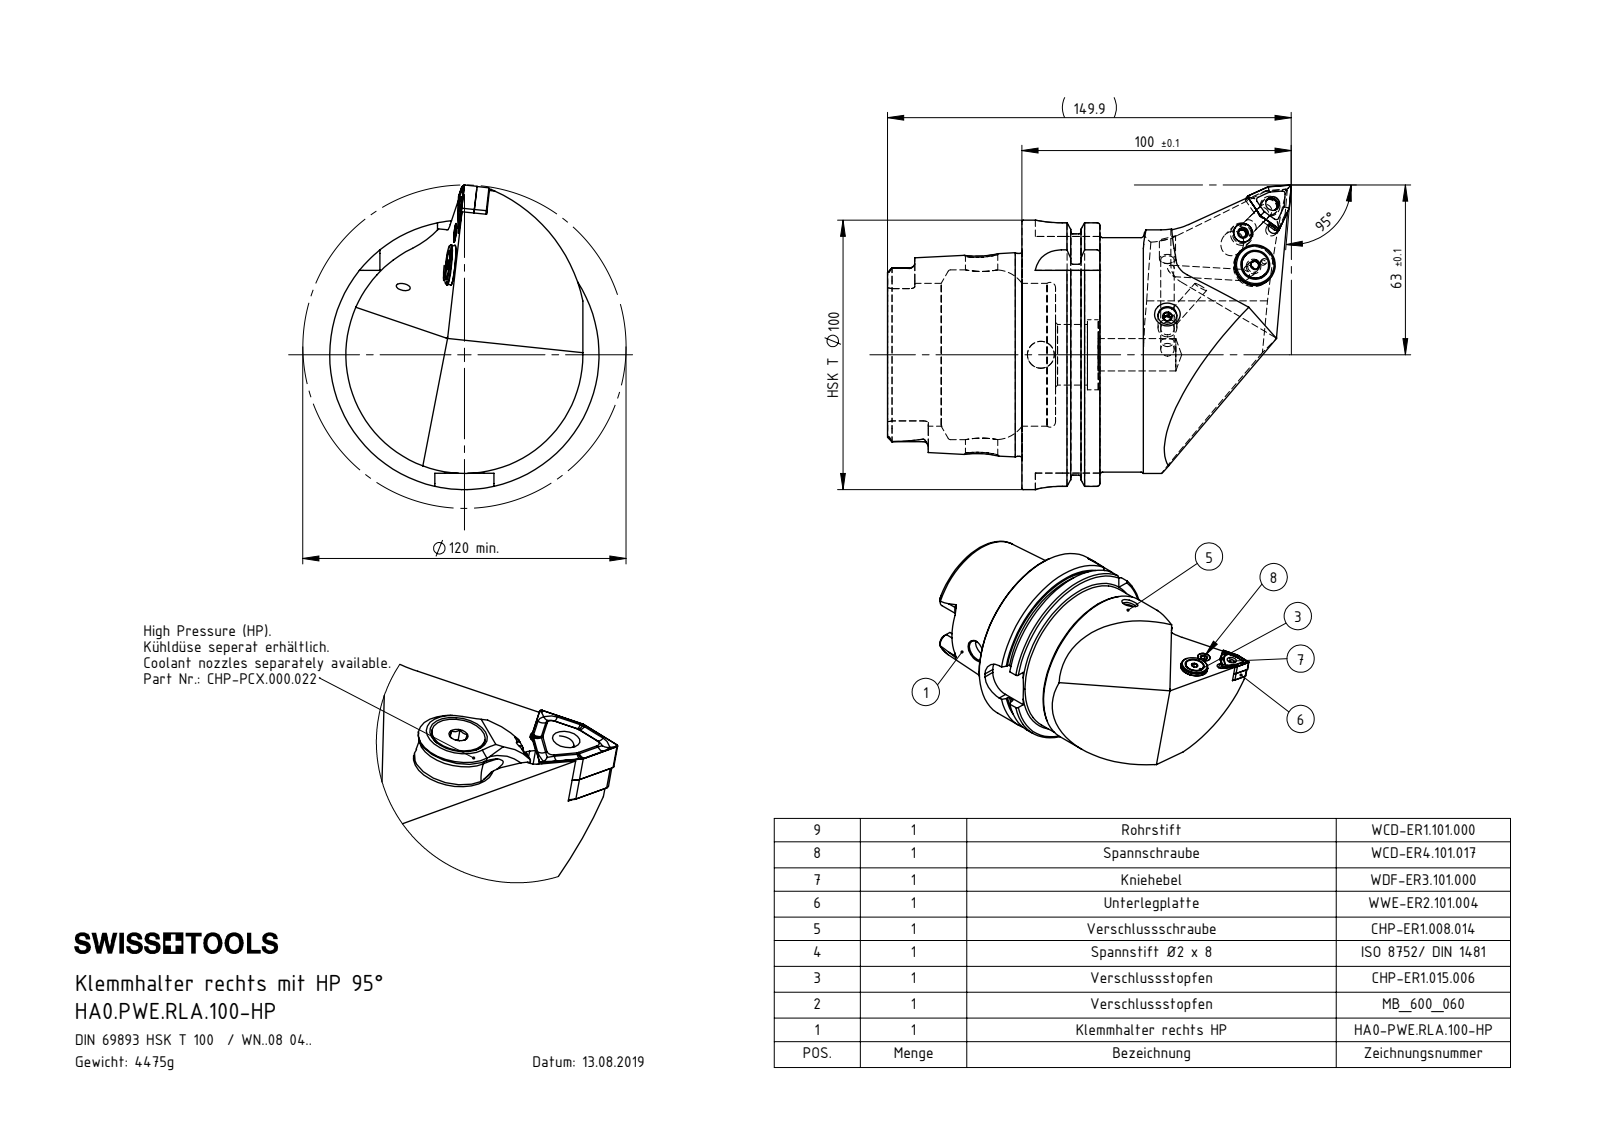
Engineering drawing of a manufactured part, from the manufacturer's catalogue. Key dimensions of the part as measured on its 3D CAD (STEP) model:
Part name (STEP PRODUCT): HA0-PWE.RLA.100-HP_A_Fertigbearbeitung; WNMG080404; WWE-ER2.101.004_A; CHP-ER1.015.006 (+8 more)
STEP written by: SolidWorks 2017 (AUTOMOTIVE_DESIGN)
Units: millimetres
Bodies: 13 solids, 395 faces (166 planar, 91 cylindrical, 138 other)
Overall size (bounding box): 149.9 × 113 × 100
Volume: 569 185 mm³ · Surface area: 75 412 mm²
Round holes (diameter × count): ⌀5 ×4, ⌀4.2 ×2, ⌀7 ×2, ⌀12 ×2, ⌀1.2 ×1, ⌀2 ×1, ⌀2.5 ×1, ⌀3 ×1, ⌀5.16 ×1, ⌀5.2 ×1, ⌀6 ×1, ⌀6.7 ×1
Round bosses / shafts (diameter × count): ⌀8 ×2, ⌀100 ×1, ⌀91.95 ×1, ⌀87 ×1, ⌀75.26 ×1, ⌀15 ×1, ⌀13.4 ×1, ⌀10 ×1
Partial cylindrical surfaces — rounded edges, fillets, slot ends (radius × count): R1.9 ×6, R10 ×4, R0.4 ×3, R1 ×3, R2.5 ×3, R0.5 ×2, R4.83 ×2, R4.88 ×2
Main face-to-face distances: 12.45, 28.95, 16.5, 49.9, 62.35, 78.85, 87.8, 78.2, 28.3, 15.85
Hole centre spacings: 4.5, 12.84, 13.09, 21.26, 15.6, 24.05, 24.06
